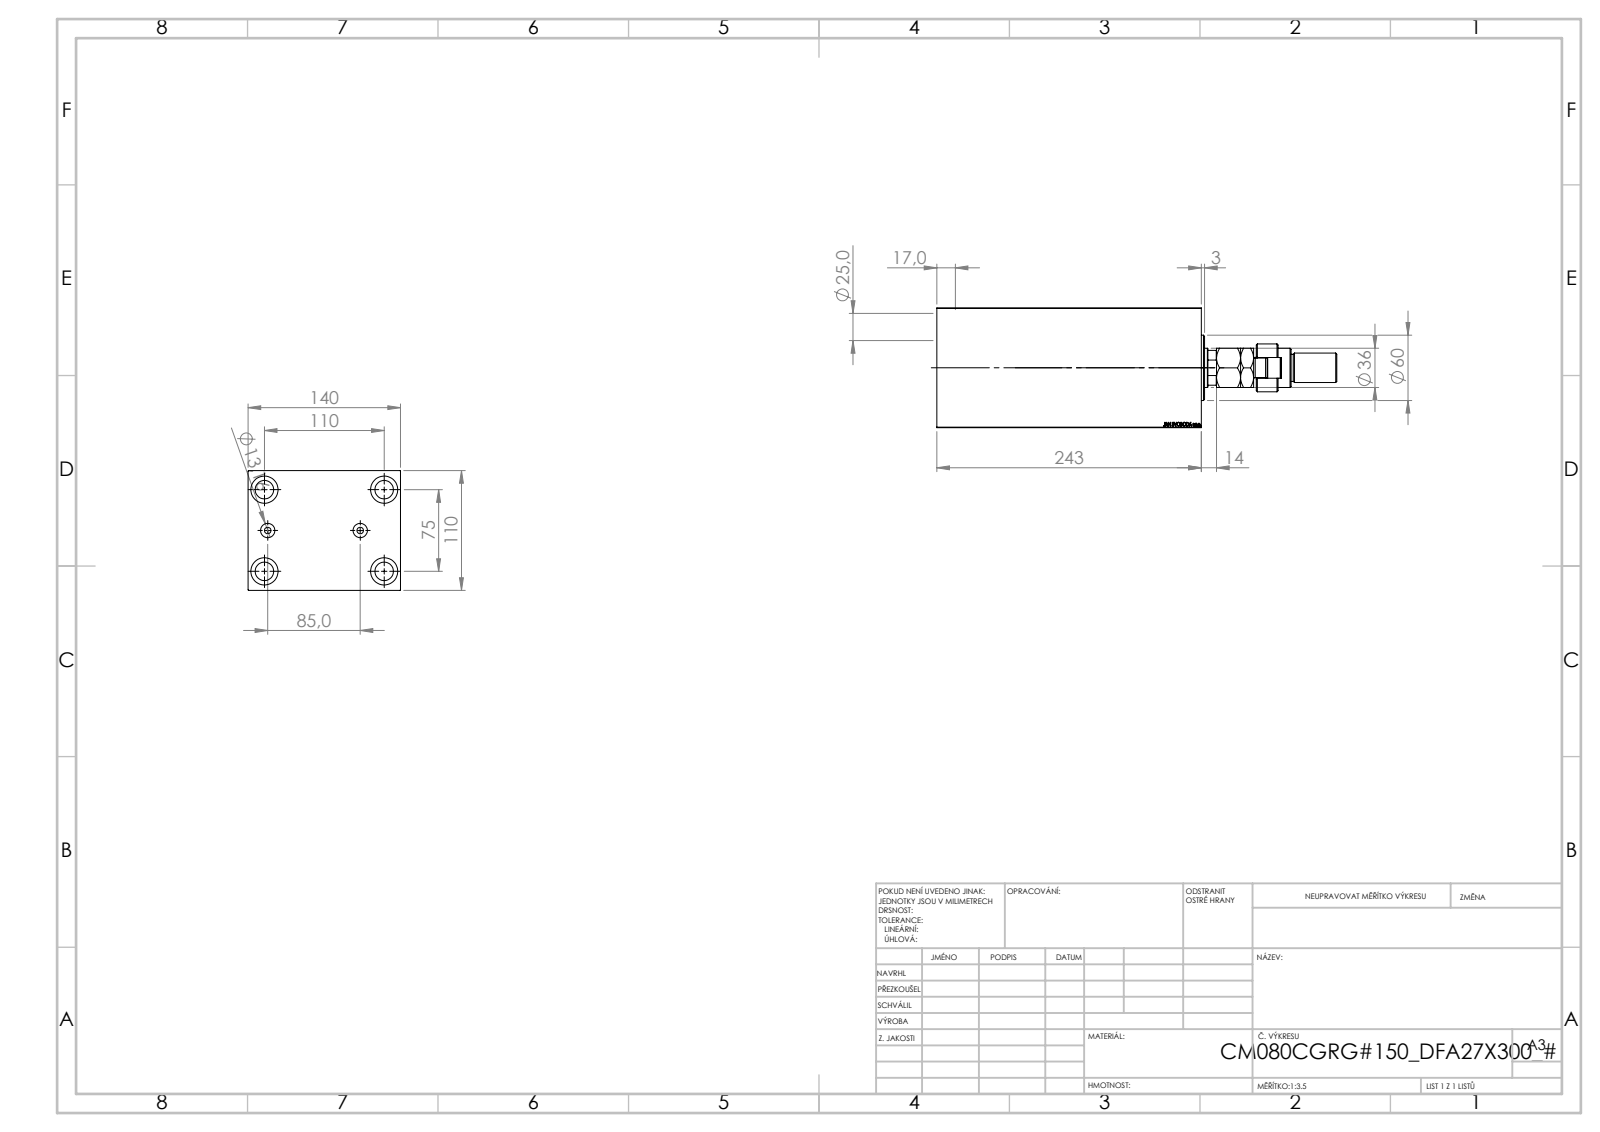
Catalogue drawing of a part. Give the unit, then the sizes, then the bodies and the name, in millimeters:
Units: millimetres
Overall size (bounding box): 367.5 × 140 × 110
Round holes (diameter × count): ⌀17 ×4, ⌀25 ×4, ⌀6 ×2, ⌀13.16 ×2, ⌀25.5 ×1, ⌀39.5 ×1, ⌀80 ×1, ⌀82 ×1, ⌀87 ×1
Round bosses / shafts (diameter × count): ⌀60 ×1, ⌀44 ×1, ⌀36 ×1, ⌀28 ×1, ⌀27 ×1, ⌀25 ×1, ⌀18 ×1
Partial cylindrical surfaces — rounded edges, fillets, slot ends (radius × count): R9.5 ×1, R15 ×1, R17.5 ×1
Main face-to-face distances: 110, 140, 243, 183.25, 59.75, 10, 233, 83, 173.25, 160
Hole centre spacings: 39.53, 66.57, 104.46, 42.5, 75, 110, 133.14, 85
Volume: 2 968 000 mm³ · Surface area: 332 353 mm²
Bodies: 5 solids, 948 faces (439 planar, 71 cylindrical, 438 other)
Part name (STEP PRODUCT): FEMALE_PART_FOR_DFA; V450CM_VC_B; MFA; V450CM_C_Body (+1 more)
STEP written by: SolidWorks 2019 (CONFIG_CONTROL_DESIGN)
